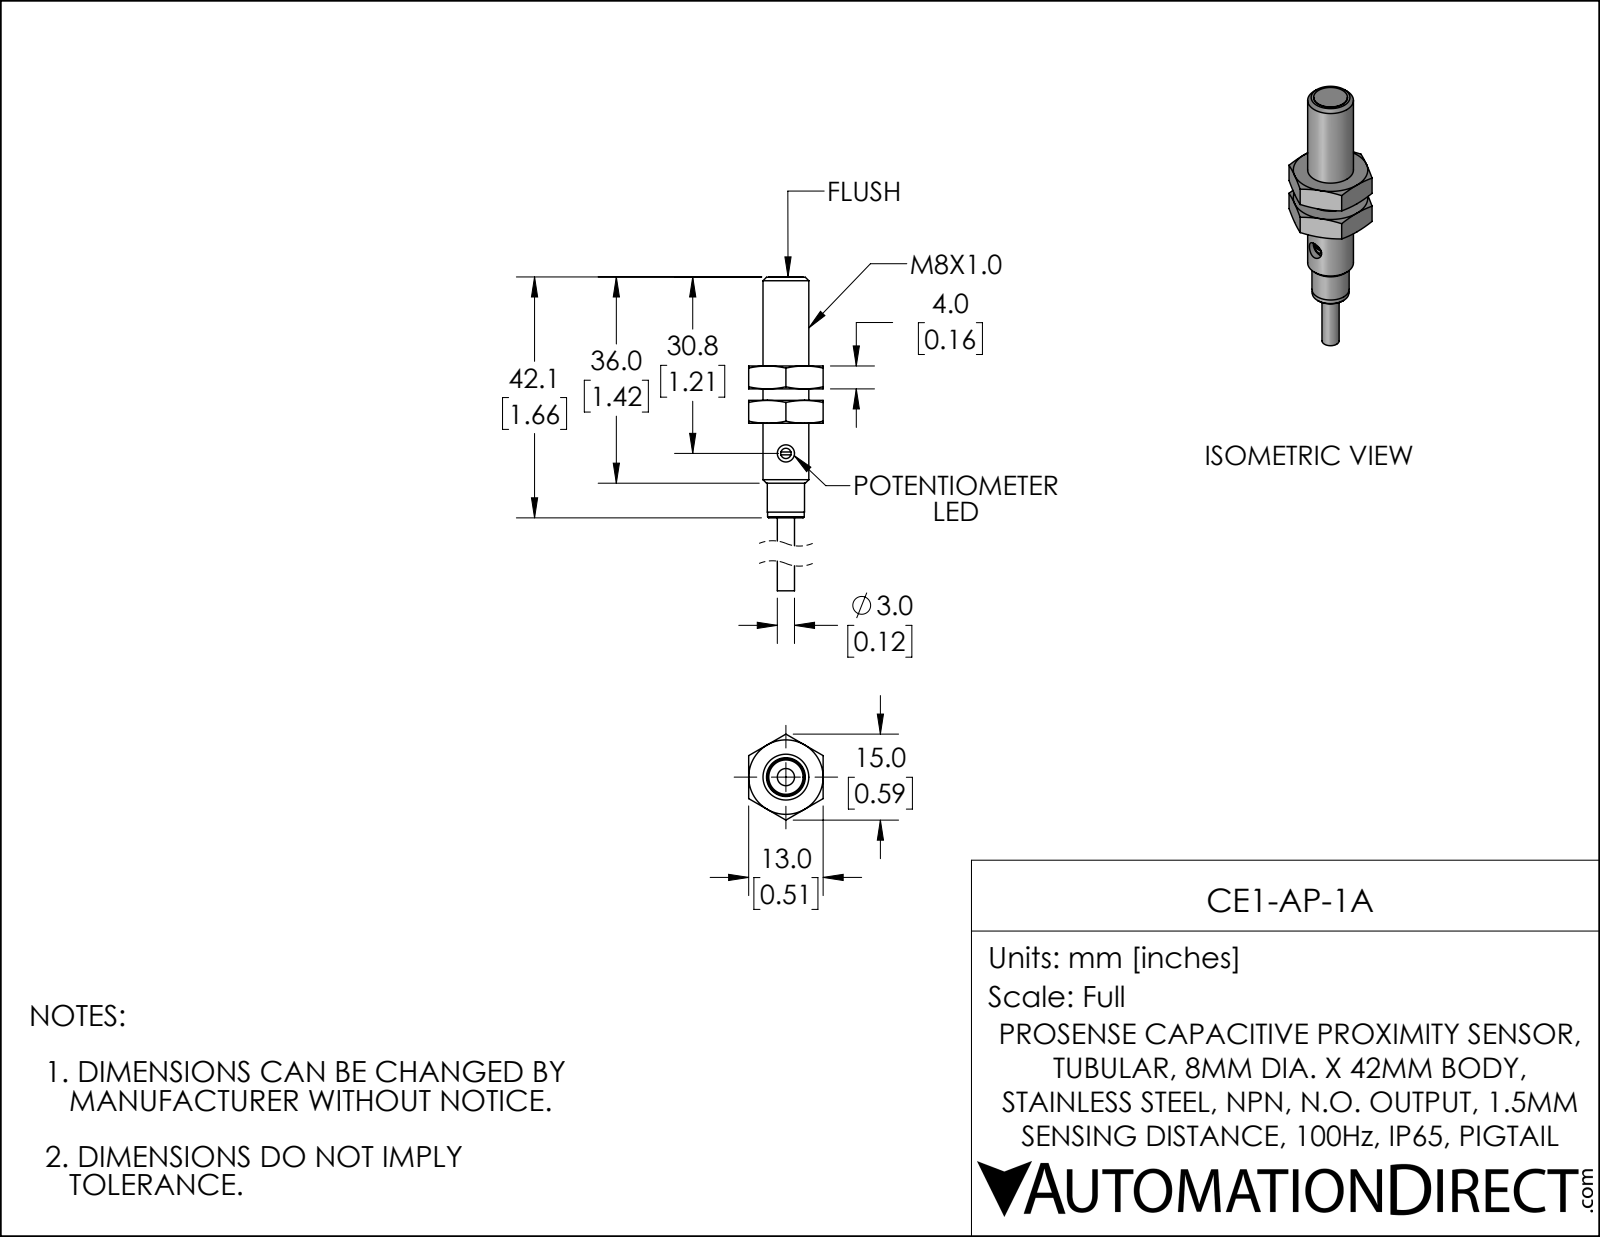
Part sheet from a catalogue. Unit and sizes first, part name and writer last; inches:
Units: inches
Overall size (bounding box): 2.049 × 0.591 × 0.512
Round holes (diameter × count): ⌀0.118 ×1, ⌀0.272 ×1
Round bosses / shafts (diameter × count): ⌀0.315 ×1, ⌀0.256 ×1, ⌀0.252 ×1, ⌀0.232 ×1, ⌀0.118 ×1, ⌀0.071 ×1
Main face-to-face distances: 0.512, 0.236, 0.157, 0.394, 0.079, 1.044, 0.612, 0.769, 0.848, 1.006
Volume: 0.178 in³ · Surface area: 3.313 in²
Bodies: 3 solids, 68 faces (28 planar, 9 cylindrical, 31 other)
Part name (STEP PRODUCT): CE1-AP-1A
STEP written by: SolidWorks 2019 (CONFIG_CONTROL_DESIGN)
